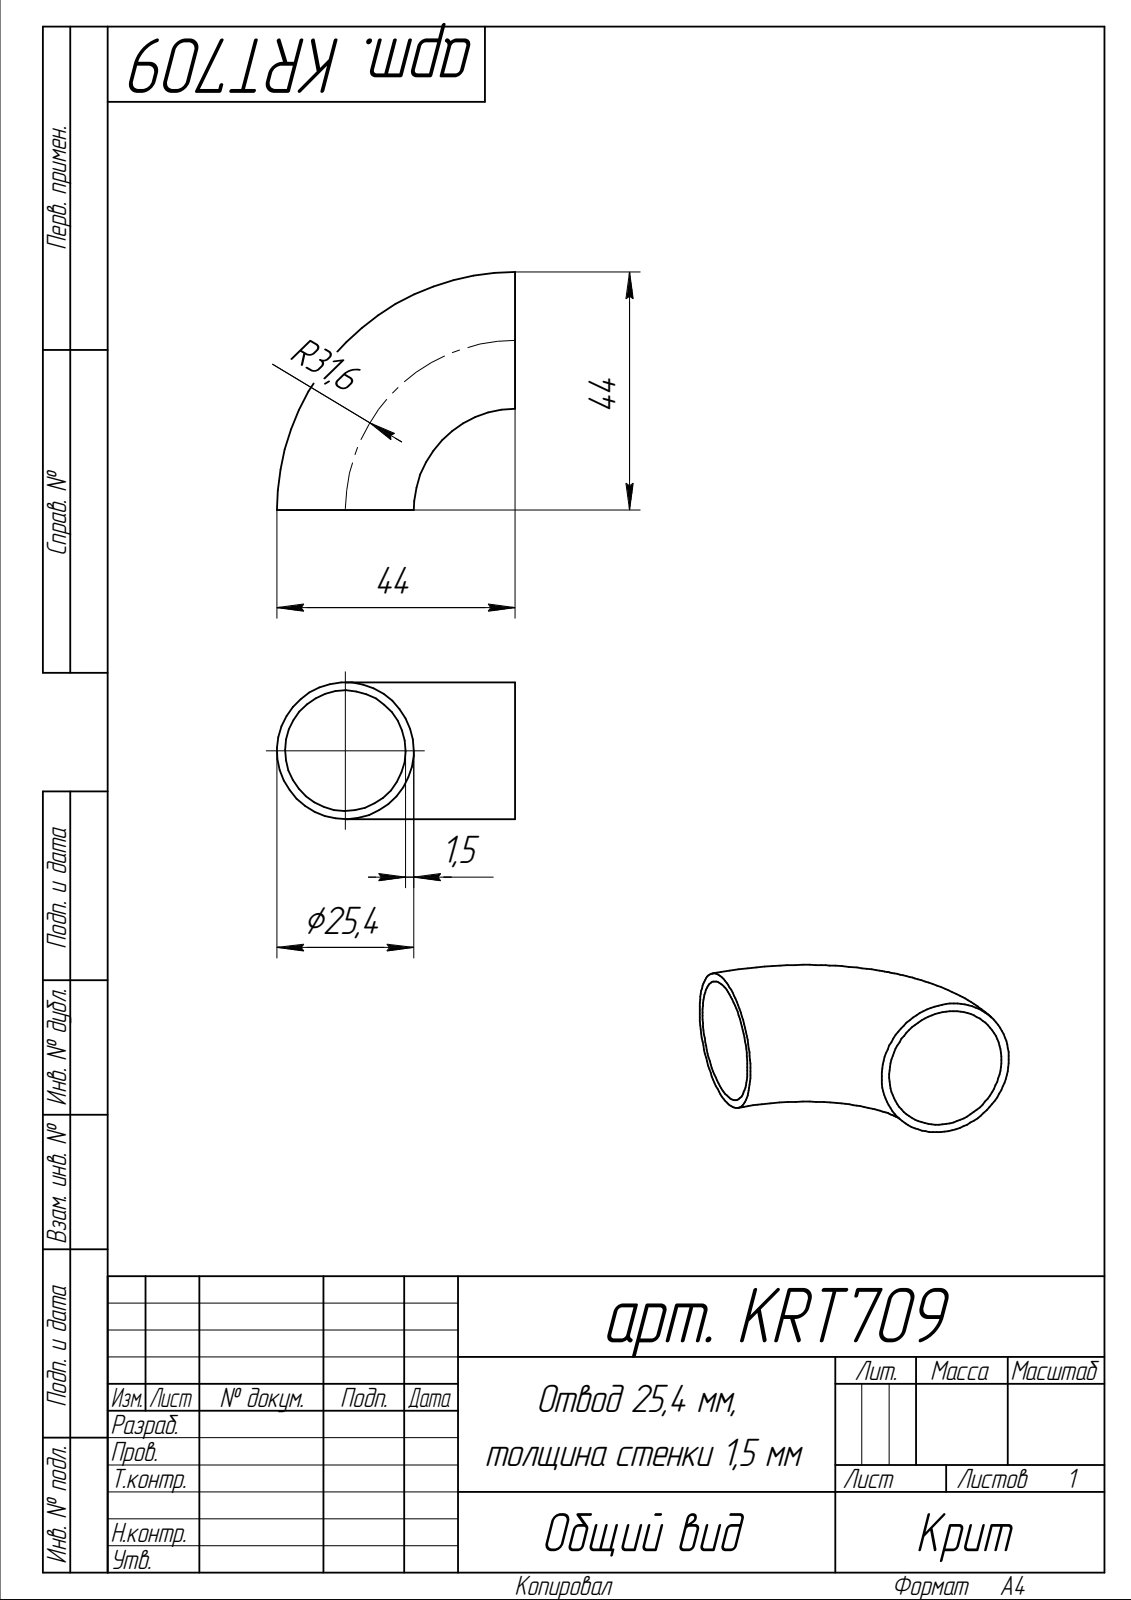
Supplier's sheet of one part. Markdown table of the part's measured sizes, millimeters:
| quantity | value |
| --- | --- |
| part name | арт. KRT709 |
| STEP written by | SolidWorks 2014 (AUTOMOTIVE_DESIGN) |
| units | millimeters |
| bodies | 1 solid, 6 faces (2 planar, 0 cylindrical, 4 other) |
| overall size | 44.2 × 44.2 × 25.4 |
| volume | 5 571 mm³ |
| surface area | 7 654 mm² |
